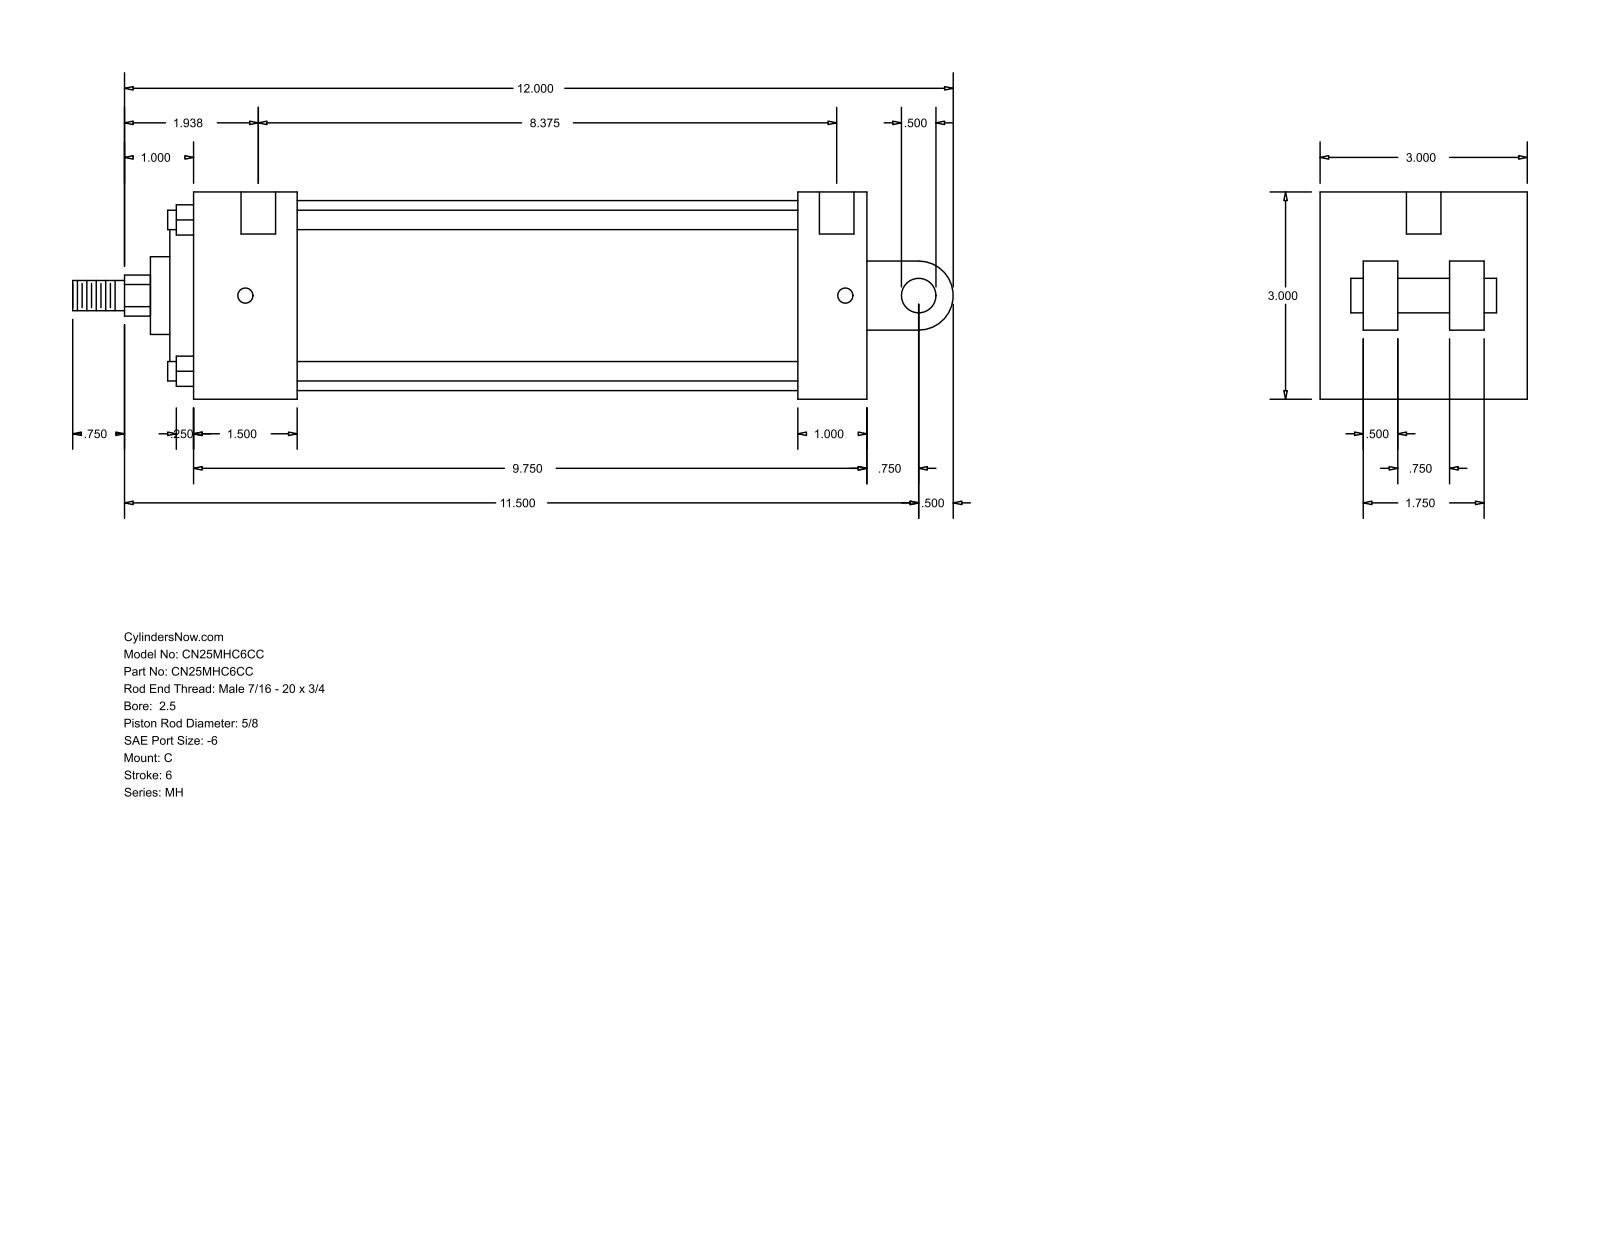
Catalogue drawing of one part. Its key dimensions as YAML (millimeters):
part_name: "MH_C__0250_0.625"
step_written_by: "GSSL Pune (CONFIG_CONTROL_DESIGN)"
units: millimeters
bodies: {solids: 0, faces: 101, planar: 71, cylindrical: 30, other: 0}
overall_size: [323.85, 76.2, 76.2]
round_holes:
  - {diameter: 5.56, count: 4}
  - {diameter: 12.7, count: 2}
round_bosses_or_shafts:
  - {diameter: 7.14, count: 4}
  - {diameter: 69.85, count: 1}
  - {diameter: 55.55, count: 1}
  - {diameter: 28.57, count: 1}
  - {diameter: 15.88, count: 1}
  - {diameter: 12.7, count: 1}
  - {diameter: 11.11, count: 1}
partial_cylinders:
  - {radius: 7.54, count: 1}
  - {radius: 12.7, count: 1}
face_to_face_distances: [76.2, 25.4, 247.65, 15.87, 38.1, 222.25, 184.15, 209.55, 8.73, 46.83]
hole_center_spacings: [220.66, 3.17, 4.76, 212.73, 215.9, 217.49]
